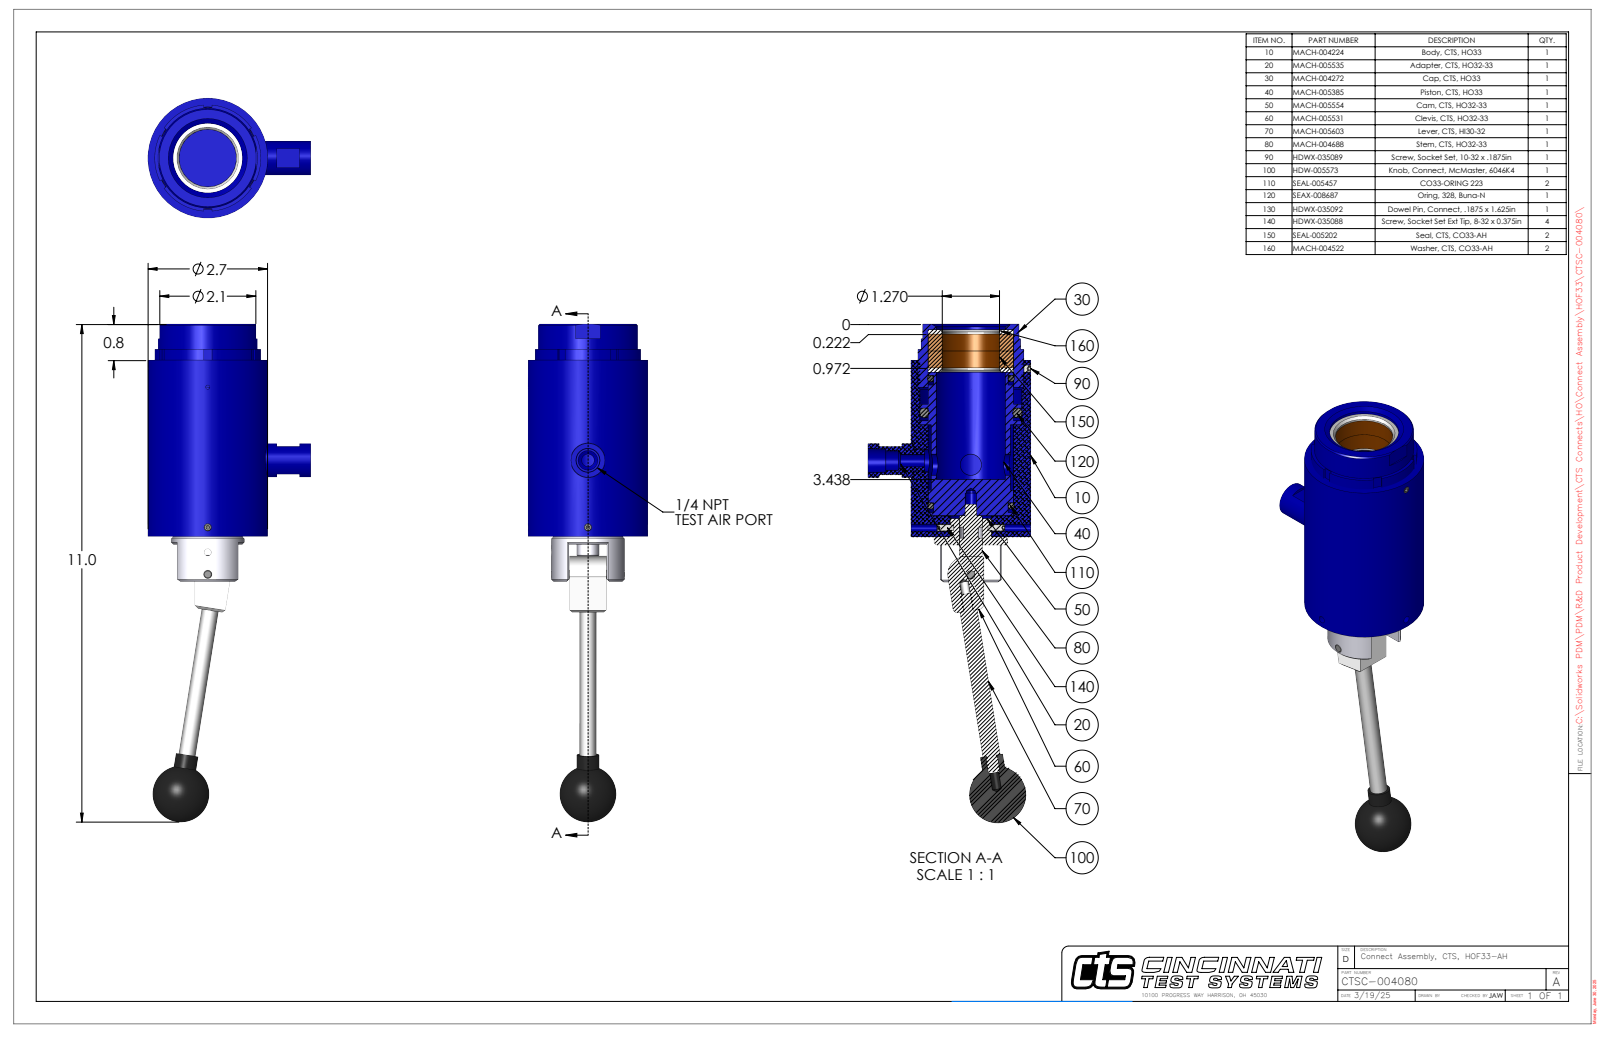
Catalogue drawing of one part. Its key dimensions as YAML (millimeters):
part_name: "CTSC-004080"
step_written_by: "SolidWorks 2023 (AUTOMOTIVE_DESIGN)"
units: millimeters
bodies: {solids: 15, faces: 546, planar: 179, cylindrical: 226, other: 141}
overall_size: [280.3, 91.4, 67.3]
volume: 357900
surface_area: 88390
round_holes:
  - {diameter: 5.1, count: 3}
  - {diameter: 4, count: 2}
  - {diameter: 11.9, count: 2}
  - {diameter: 2.4, count: 1}
  - {diameter: 4.8, count: 1}
  - {diameter: 4.8, count: 1}
  - {diameter: 6.4, count: 1}
  - {diameter: 7.1, count: 1}
  - {diameter: 11.1, count: 1}
  - {diameter: 12.7, count: 1}
  - {diameter: 13.1, count: 1}
  - {diameter: 13.6, count: 1}
round_bosses_or_shafts:
  - {diameter: 19.1, count: 2}
  - {diameter: 12.7, count: 2}
  - {diameter: 4.2, count: 2}
  - {diameter: 2.8, count: 2}
  - {diameter: 67.3, count: 1}
  - {diameter: 59.5, count: 1}
  - {diameter: 55.9, count: 1}
  - {diameter: 47.9, count: 1}
partial_cylinders:
  - {radius: 9.8, count: 1}
  - {radius: 10.2, count: 1}
  - {radius: 28.7, count: 1}
  - {radius: 30.5, count: 1}
face_to_face_distances: [21.4, 2.4, 19.1, 94.9, 113.9, 9.5, 9.5, 104.4, 11.9, 92.5]
hole_center_spacings: [2.4, 12.4, 43.5, 49.4, 51.6, 54, 61.8, 92.9]
